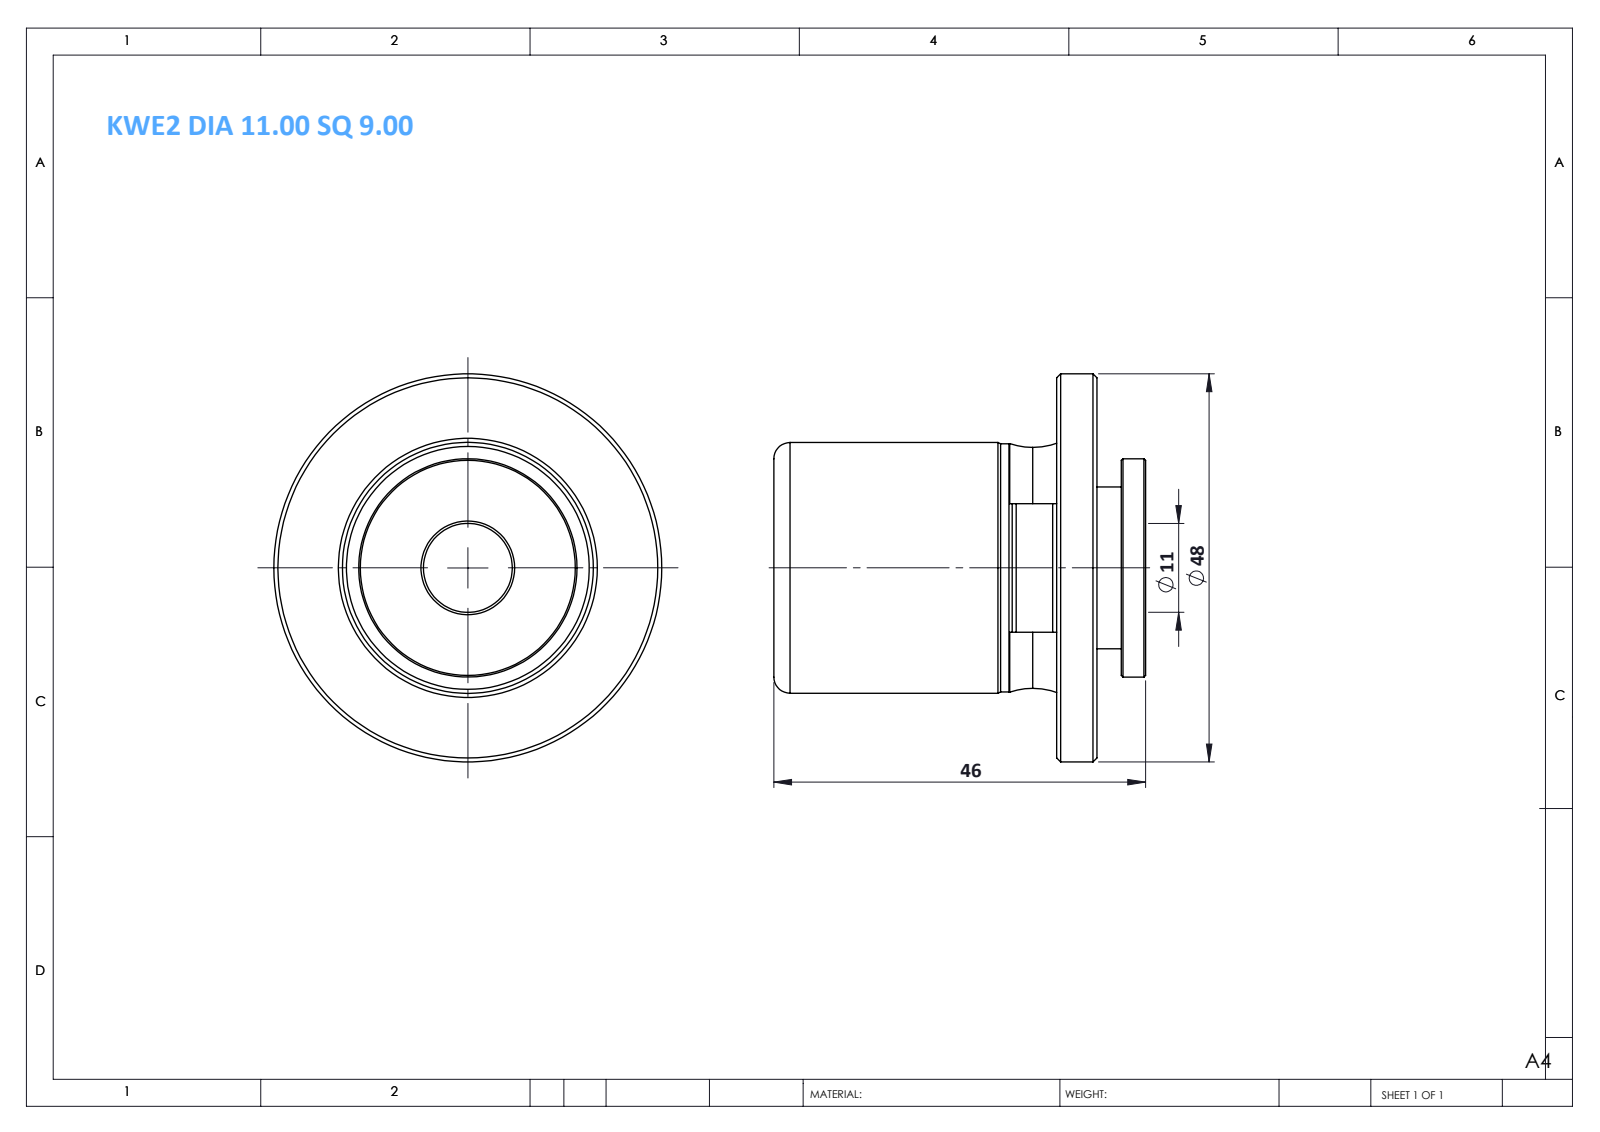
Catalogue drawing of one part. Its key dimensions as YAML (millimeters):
part_name: "KWE2 DIA 11.00 SQ 9.00"
step_written_by: "SolidWorks 2014 (CONFIG_CONTROL_DESIGN)"
units: millimeters
bodies: {solids: 1, faces: 61, planar: 13, cylindrical: 18, other: 30}
overall_size: [48, 48, 46]
volume: 35926
surface_area: 9713
round_holes:
  - {diameter: 11, count: 1}
round_bosses_or_shafts:
  - {diameter: 48, count: 1}
  - {diameter: 31, count: 1}
  - {diameter: 30.7, count: 1}
  - {diameter: 27, count: 1}
  - {diameter: 20, count: 1}
partial_cylinders:
  - {radius: 15.53, count: 1}
  - {radius: 19.9, count: 1}
face_to_face_distances: [5, 35, 40, 3, 46, 11, 6, 43, 8, 29.5]
